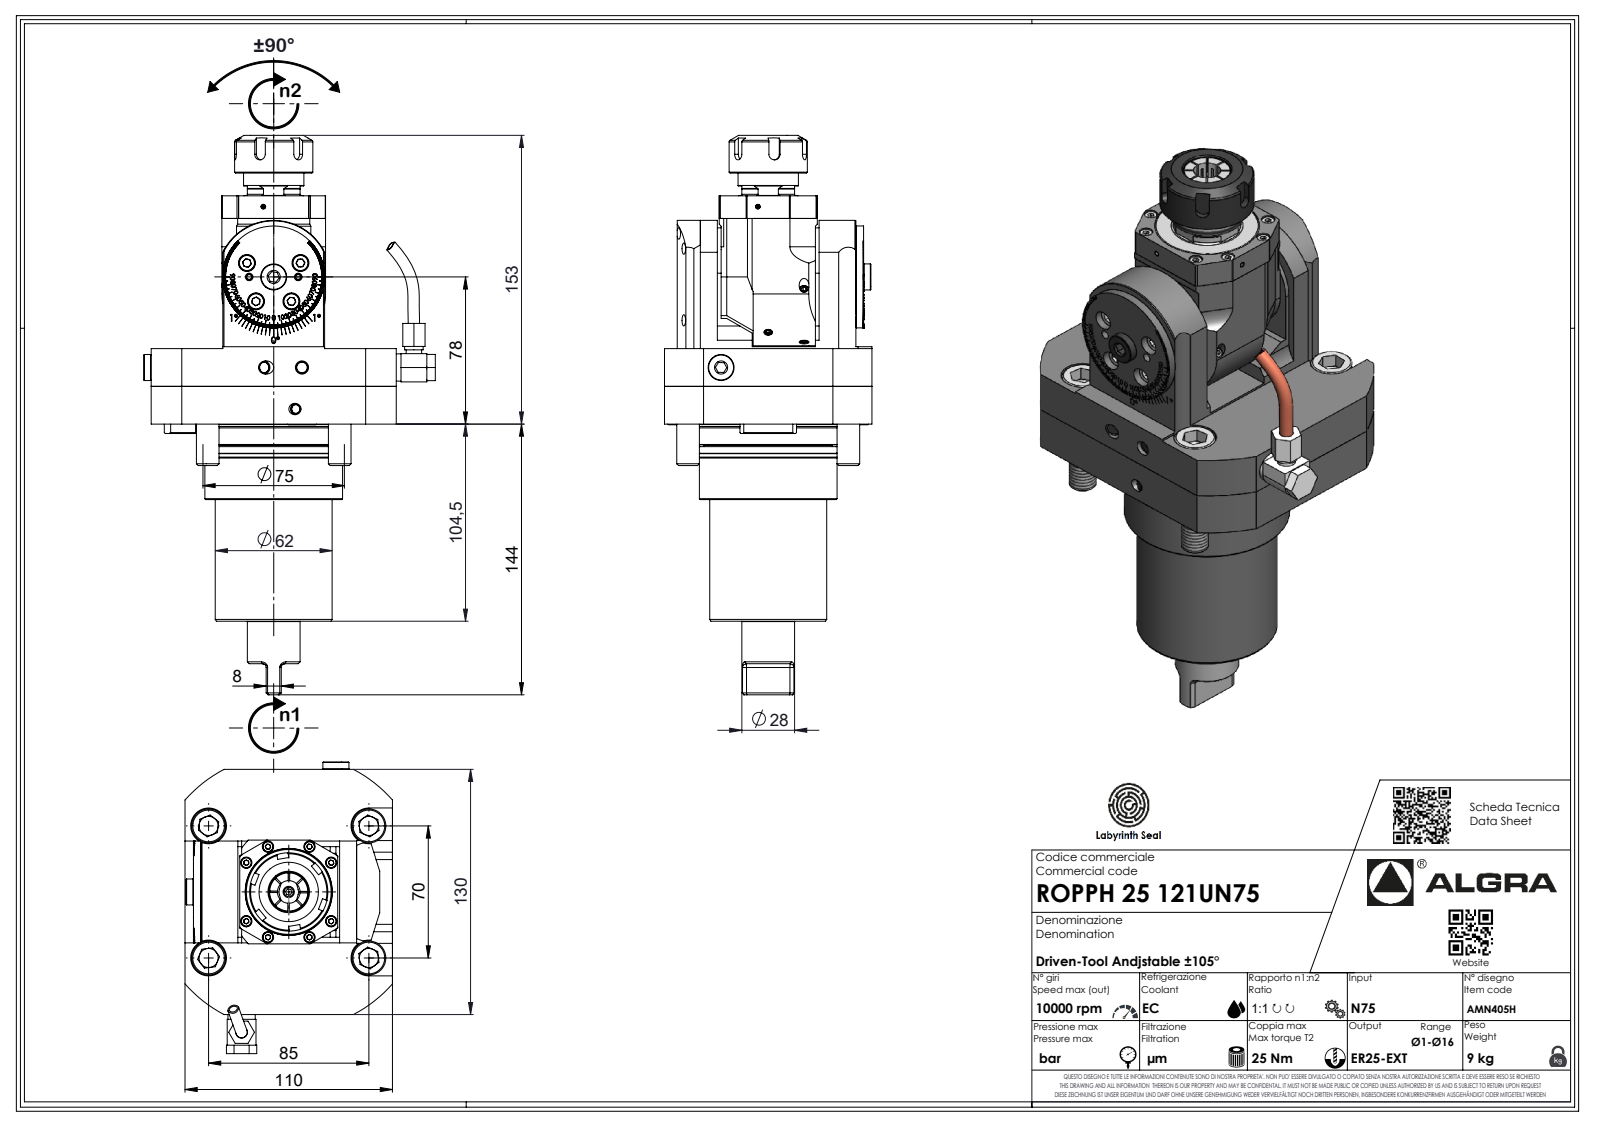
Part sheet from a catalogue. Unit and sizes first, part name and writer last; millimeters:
Units: millimetres
Overall size (bounding box): 296.53 × 150.7 × 110
Round holes (diameter × count): ⌀2.1 ×1, ⌀4 ×1
Round bosses / shafts (diameter × count): ⌀75 ×1, ⌀74.6 ×1, ⌀73 ×1, ⌀68 ×1, ⌀62 ×1, ⌀54 ×1, ⌀41.5 ×1, ⌀32 ×1
Partial cylindrical surfaces — rounded edges, fillets, slot ends (radius × count): R1 ×8, R4 ×8, R0.33 ×7, R0.52 ×7, R3.7 ×7, R2 ×6, R10 ×6, R3 ×5
Main face-to-face distances: 40, 1, 81, 80, 54.5, 38, 41, 92, 0.5, 37.5
Volume: 1 299 000 mm³ · Surface area: 114 956 mm²
Bodies: 1 solid, 634 faces (405 planar, 124 cylindrical, 105 other)
Part name (STEP PRODUCT): ROPPH25121UN75
STEP written by: SolidWorks 2023 (AUTOMOTIVE_DESIGN)
